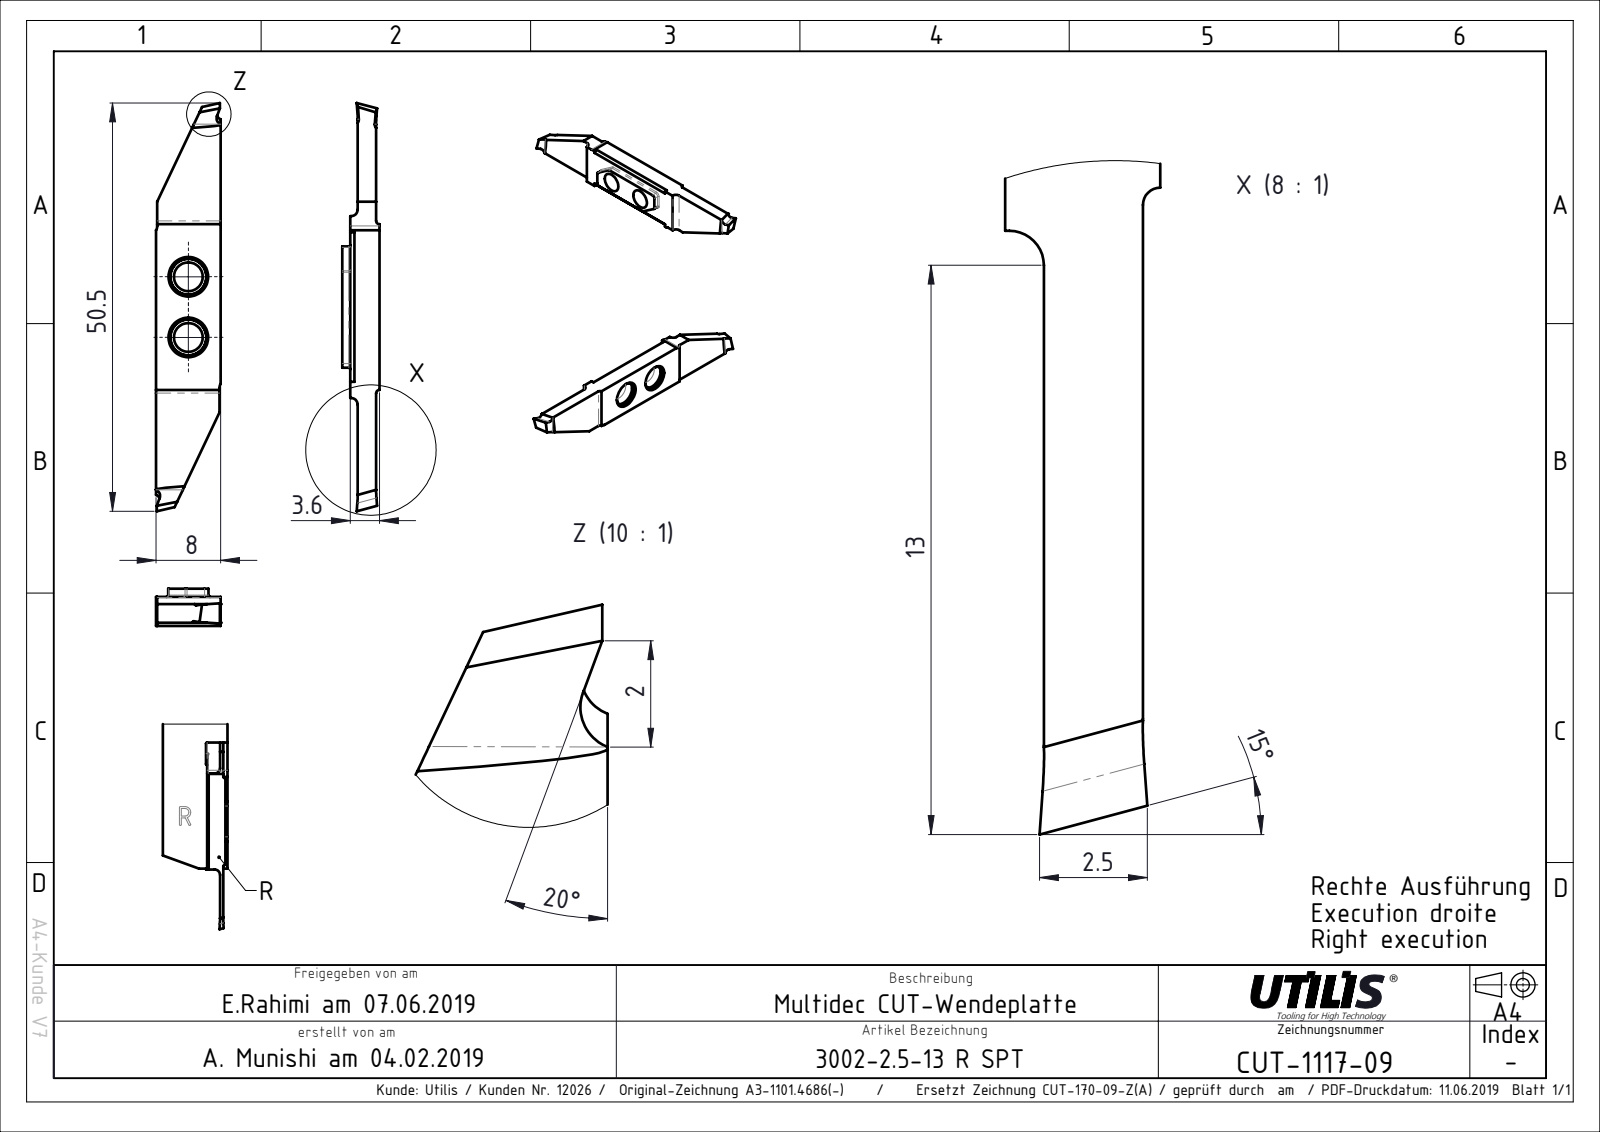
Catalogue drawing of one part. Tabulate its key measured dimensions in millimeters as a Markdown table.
| quantity | value |
| --- | --- |
| part name | CUT-1117; ASME Y14.5 |
| STEP written by | FormatWorks Professional (AP242_MANAGED_MODEL_BASED_3D_ENGINEERING_MIM_LF) |
| units | millimeters |
| bodies | 1 solid, 38 faces (28 planar, 10 cylindrical, 0 other) |
| overall size | 50.5 × 8 × 3.6 |
| volume | 906 mm³ |
| surface area | 1 002 mm² |
| round holes (diameter × count) | 3.55 × 2 |
| partial cylindrical surfaces (radius × count) | 0.4 × 2, 0.8 × 2, 1 × 2 |
| main face-to-face distances | 0.41, 3.19, 3.6, 0.91, 2.28, 2.69, 8, 18.09, 7.85, 7.7 |
| hole center spacings | 7.5 |
